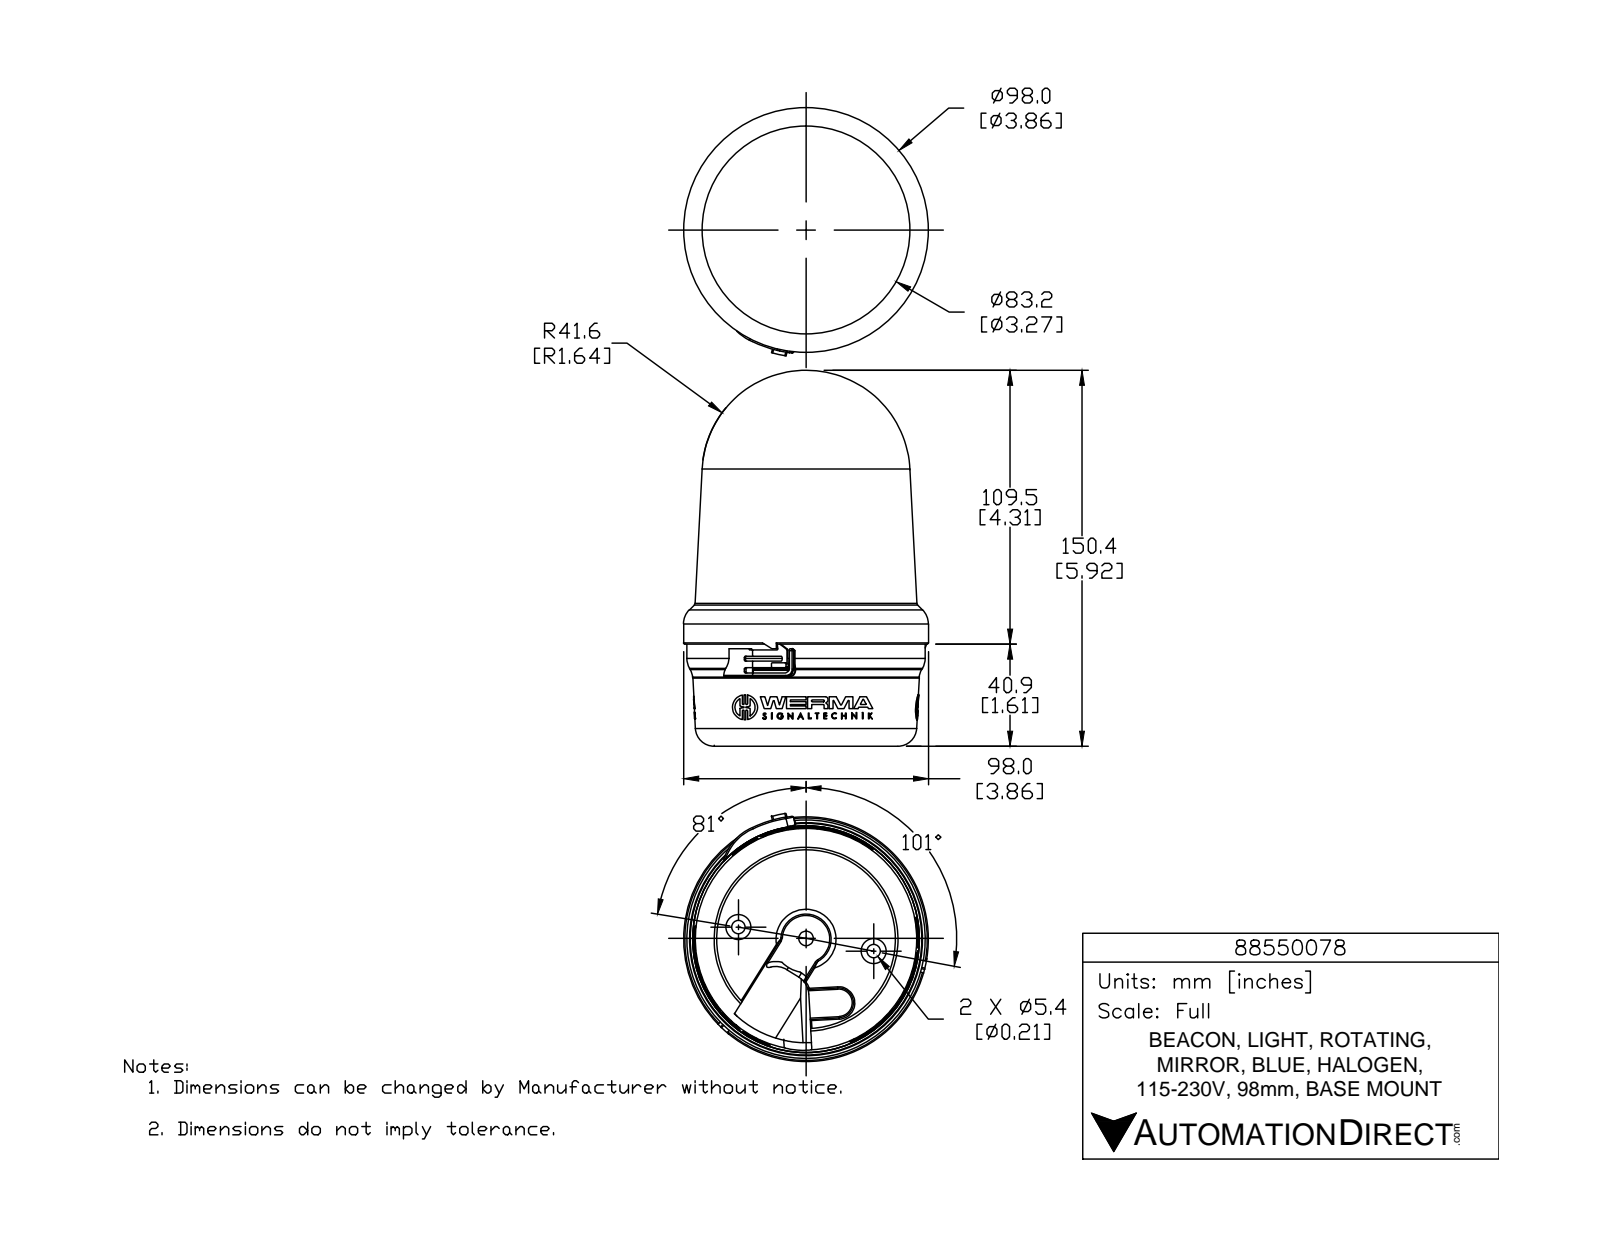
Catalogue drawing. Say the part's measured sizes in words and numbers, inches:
The part is named "88550078". Its 3-D file was written by "SolidWorks 2015 (AUTOMOTIVE_DESIGN)". It is 1 solid with 969 faces: 586 planar, 238 cylindrical and 145 other. Overall it measures 5.921 by 3.912 by 3.858 inches. Its volume is 49.51 cubic inches and its surface area 82.1 square inches. Round holes: 3 of diameter 0.068, 2 of diameter 0.213, 2 of diameter 0.409, 1 of diameter 2.815. Round bosses or shafts: 3 of diameter 0.395, 3 of diameter 0.099, 2 of diameter 0.394, 1 of diameter 3.858, 1 of diameter 3.756, 1 of diameter 3.571. Partial cylindrical surfaces (rounded edges, fillets, slot ends): 21 of radius 0.02, 9 of radius 0.006, 6 of radius 0.006, 6 of radius 0.014, 6 of radius 0.014, 6 of radius 0.014, 6 of radius 0.229, 4 of radius 0.079. The main face-to-face distances are 0.059, 0.033, 0.27, 0.02, 0.289, 0.734, 0.768, 0.315, 1.319, 1.26. The hole center spacings are 1.083, 2.165.
